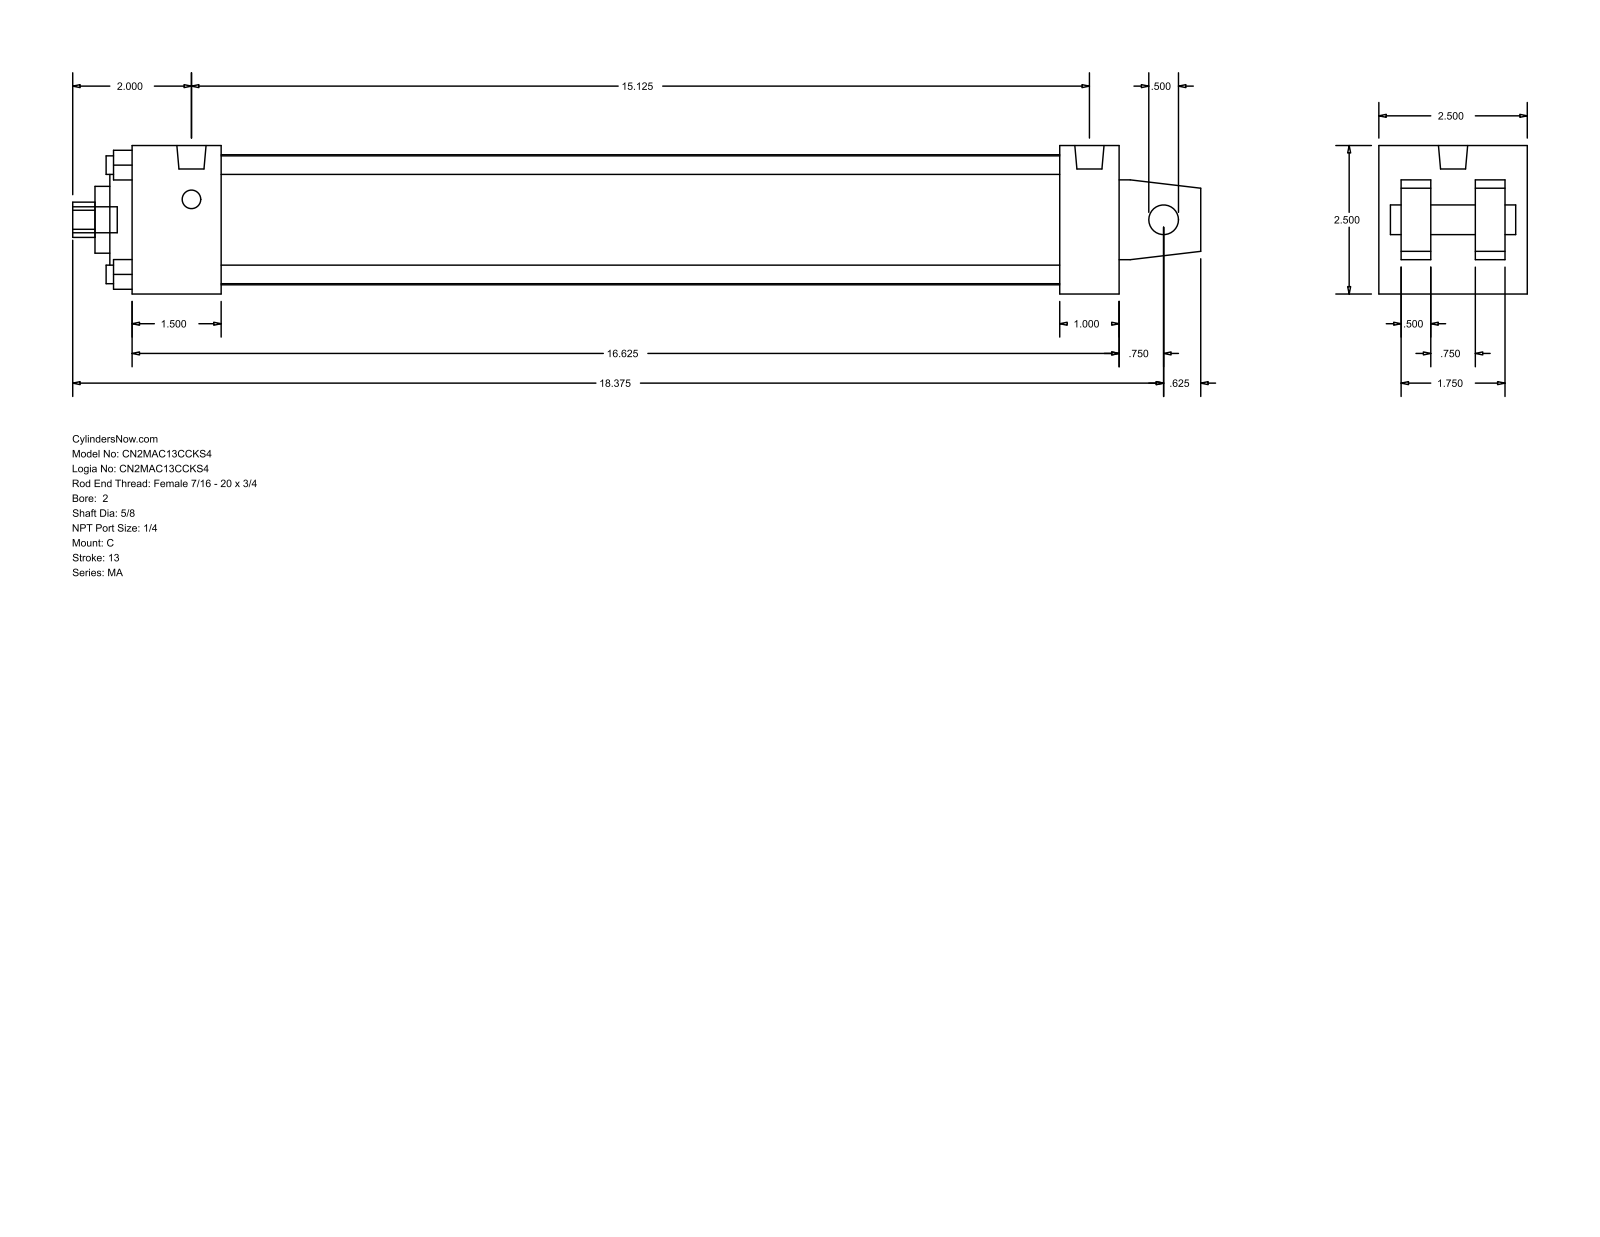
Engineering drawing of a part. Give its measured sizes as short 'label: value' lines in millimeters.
name: MA_C__0200_0.625
written by: GSSL Pune (CONFIG_CONTROL_DESIGN)
unit: mm
bodies: 0 solids, 105 faces (77 planar, 28 cylindrical, 0 other)
size: 482.6 × 63.5 × 63.5
holes: 4× ⌀7.94, 1× ⌀12.7, 1× ⌀15.88, 1× ⌀28.57, 1× ⌀50.8, 1× ⌀55.63
bosses: 4× ⌀7.94, 2× ⌀12.49, 1× ⌀11.11
rounds: 1× R7.54
face distances: 63.5, 9.52, 12.7, 22.22, 41.28, 53.98, 31.76, 38.1, 422.28, 384.18
hole spacings: 33.05, 46.74, 66.1
